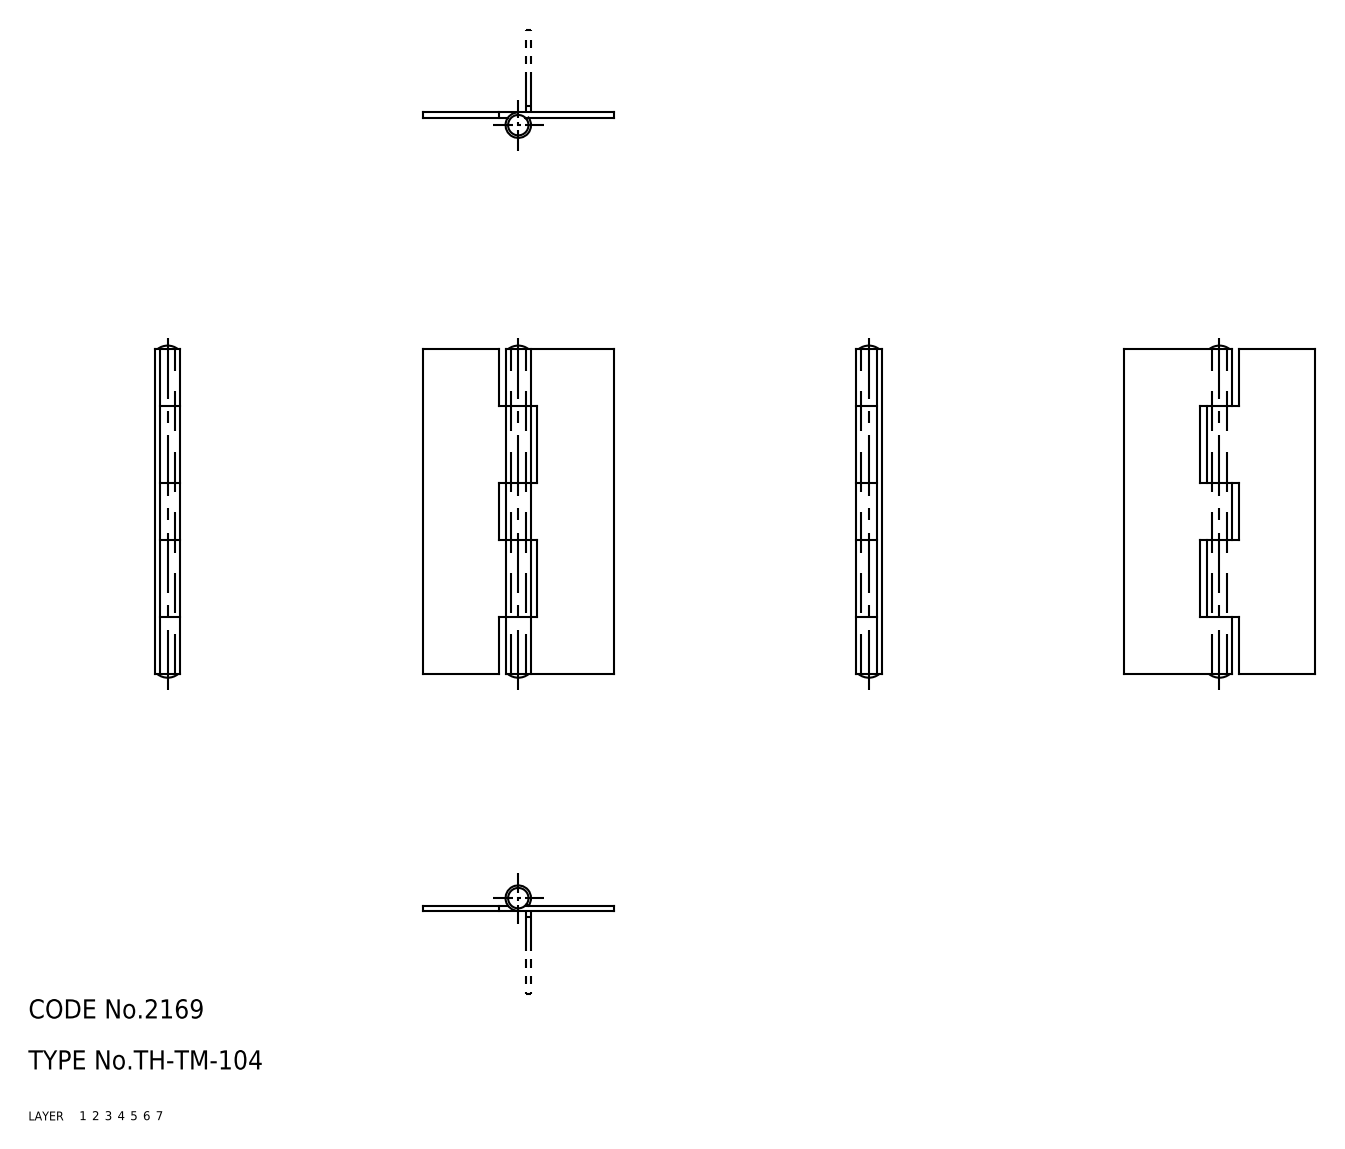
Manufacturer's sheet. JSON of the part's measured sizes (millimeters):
{"part_name": "67110963; 67110976; 67110989", "step_written_by": "CADfix (AUTOMOTIVE_DESIGN)", "units": "millimeters", "bodies": {"solids": 3, "faces": 44, "planar": 0, "cylindrical": 0, "other": 44}, "overall_size": [52.5, 30, 4], "volume_mm3": 1687, "surface_area_mm2": 4328}
